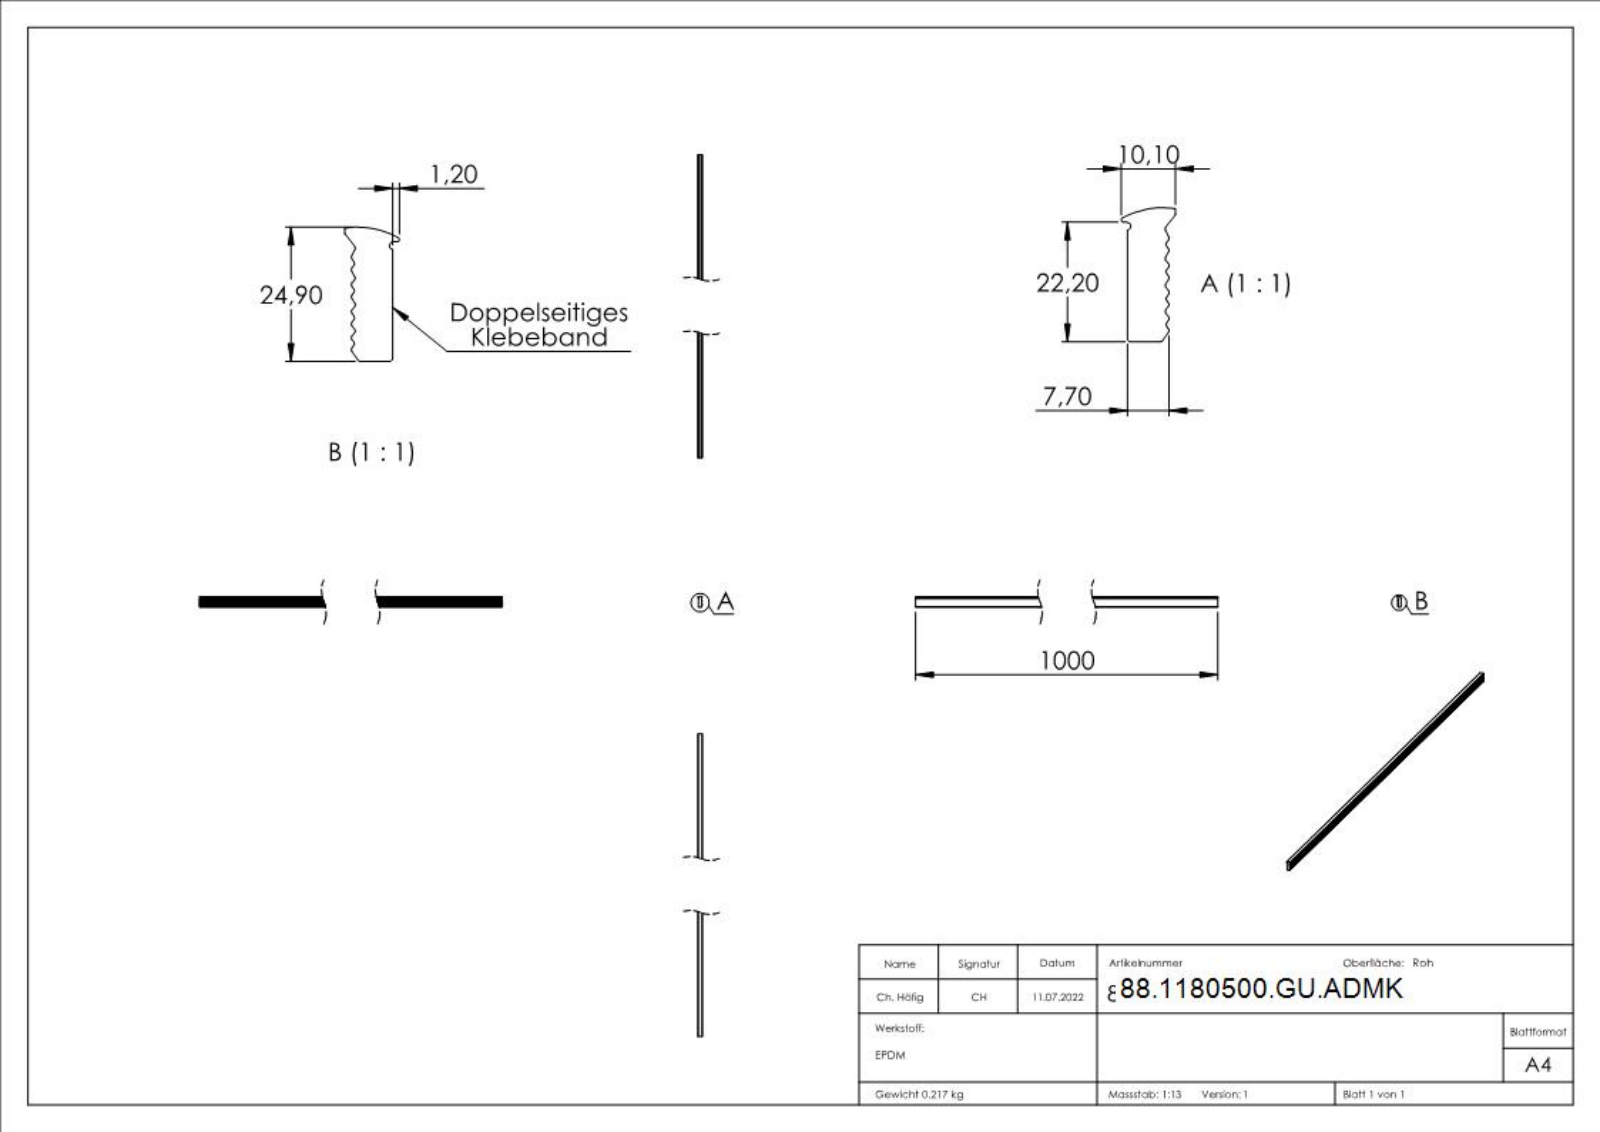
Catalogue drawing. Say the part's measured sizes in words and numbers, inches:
The part is named "80500-GU-ADMK". Its 3-D file was written by "SolidWorks 2018 (CONFIG_CONTROL_DESIGN)". It is 1 solid with 363 faces: 196 planar, 24 cylindrical and 143 other. Overall it measures 39.37 by 0.98 by 0.398 inches. Its volume is 11.2 cubic inches and its surface area 107.9 square inches. Partial cylindrical surfaces (rounded edges, fillets, slot ends): 18 of radius 0.024, 3 of radius 0.008, 1 of radius 0.017, 1 of radius 0.028, 1 of radius 0.624. The main face-to-face distances are 0.35, 0.874, 0.065, 39.37, 0.346, 0.124, 0.3, 0.186, 0.013, 0.172.
